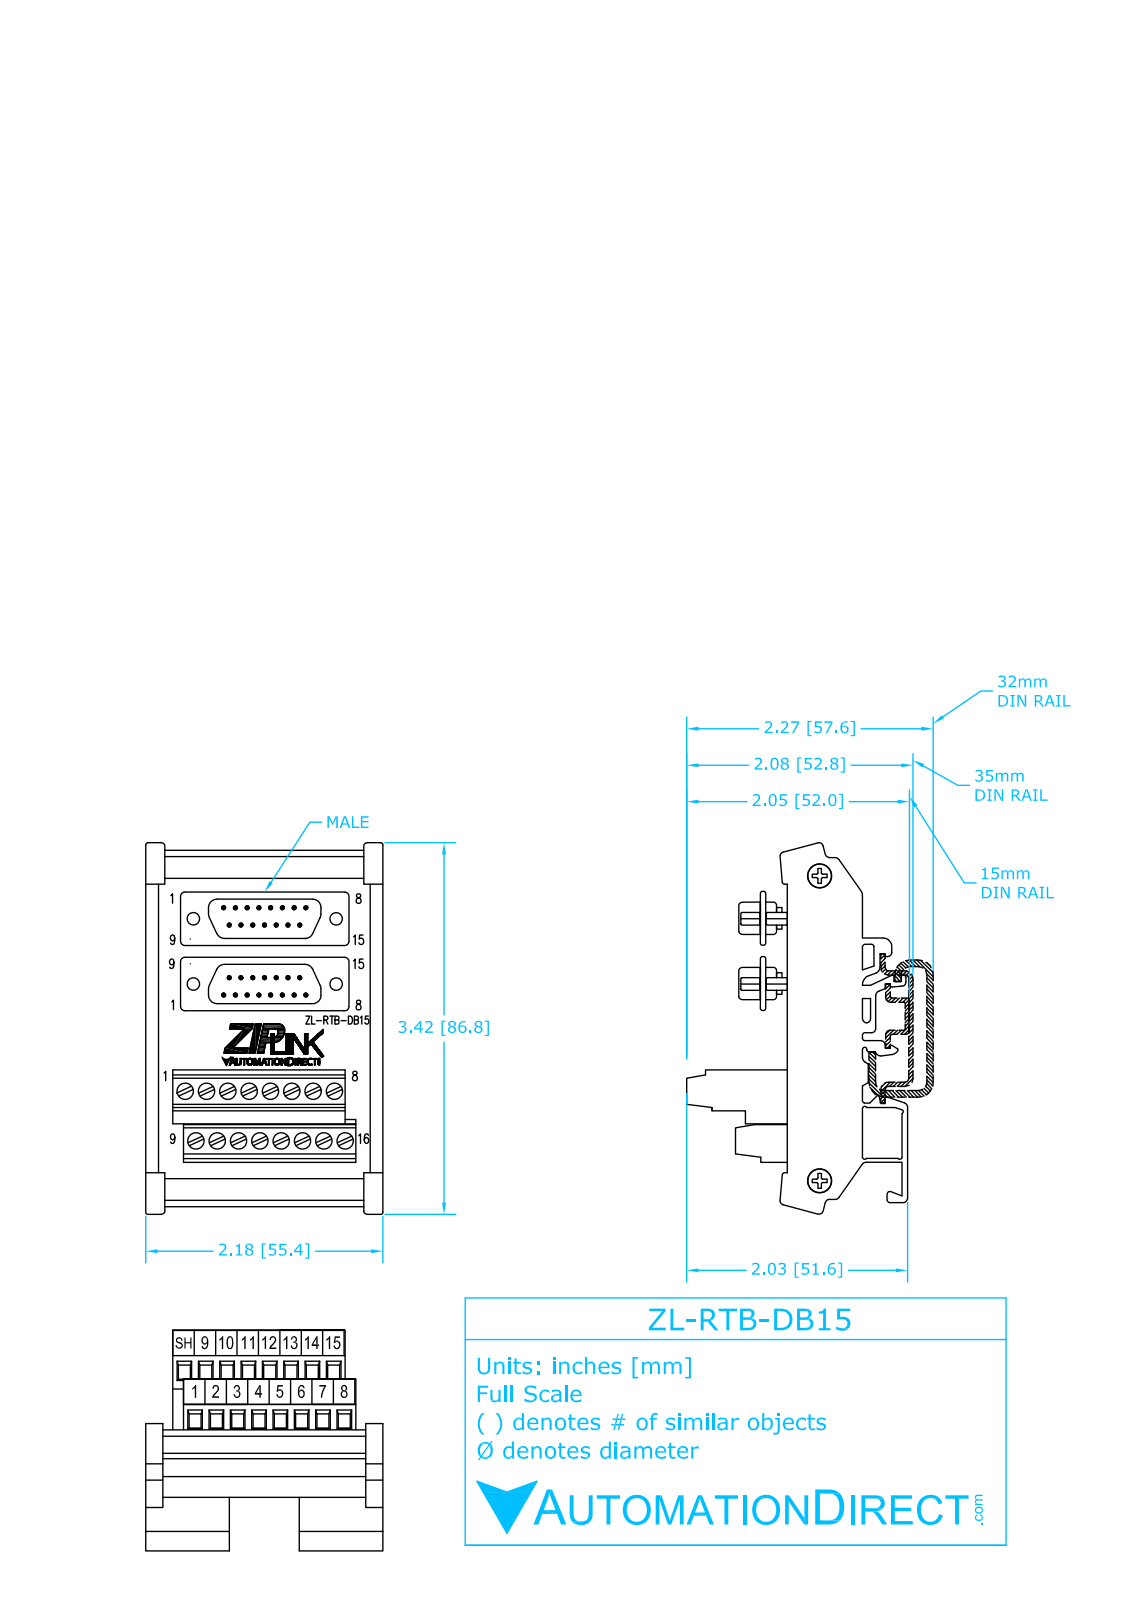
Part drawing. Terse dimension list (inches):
name: ZL-RTB-DB15
written by: SolidWorks 2014 (AUTOMOTIVE_DESIGN)
unit: in
bodies: 1 solid, 912 faces (647 planar, 257 cylindrical, 8 other)
size: 3.42 × 2.236 × 2.03
volume: 5.877 in³; area: 49.92 in²
holes: 16× ⌀0.15, 14× ⌀0.055, 4× ⌀0.089, 2× ⌀0.225, 1× ⌀0.055
bosses: 14× ⌀0.035, 2× ⌀0.205, 1× ⌀0.035
rounds: 41× R0.015, 10× R0.03, 8× R0.06, 8× R0.08, 8× R0.1
face distances: 2.18, 0.03, 0.628, 0.658, 0.452, 1.08, 1.11, 0.25, 0.02, 0.93
hole spacings: 0.1, 0.2, 0.3, 0.125, 0.196, 0.125, 0.189, 0.4
